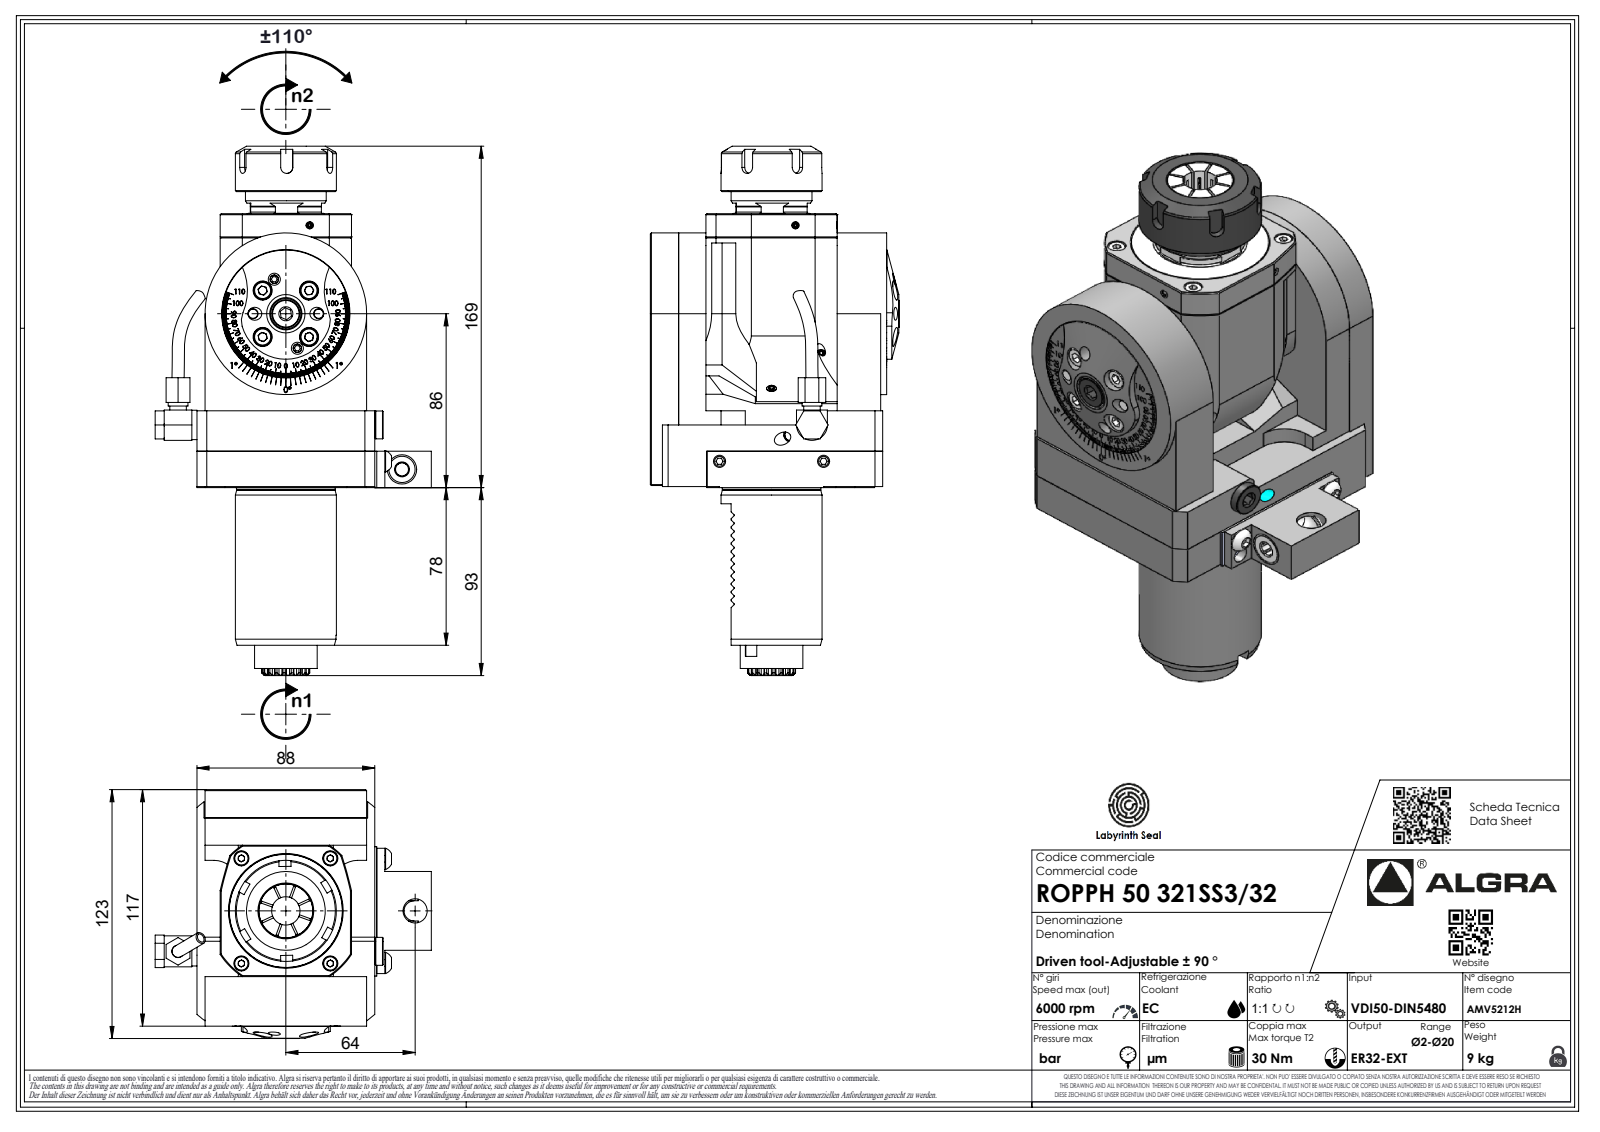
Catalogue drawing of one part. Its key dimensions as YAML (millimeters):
part_name: "ROPPH50321SS332"
step_written_by: "SolidWorks 2023 (AUTOMOTIVE_DESIGN)"
units: millimeters
bodies: {solids: 1, faces: 762, planar: 424, cylindrical: 150, other: 188}
overall_size: [261.91, 136.7, 123]
volume: 1279000
surface_area: 111521
round_holes:
  - {diameter: 2.1, count: 1}
  - {diameter: 31, count: 1}
round_bosses_or_shafts:
  - {diameter: 80, count: 1}
  - {diameter: 50, count: 1}
  - {diameter: 48.7, count: 1}
  - {diameter: 40, count: 1}
  - {diameter: 14.5, count: 1}
  - {diameter: 9.8, count: 1}
  - {diameter: 8.2, count: 1}
  - {diameter: 6.37, count: 1}
partial_cylinders:
  - {radius: 1.61, count: 36}
  - {radius: 0.3, count: 12}
  - {radius: 0.33, count: 7}
  - {radius: 0.52, count: 7}
  - {radius: 3.7, count: 7}
  - {radius: 3, count: 5}
  - {radius: 10, count: 2}
  - {radius: 12, count: 2}
face_to_face_distances: [4, 65, 84, 0.5, 11.5, 72.5, 76.5, 7.5, 27.5, 89.5]
